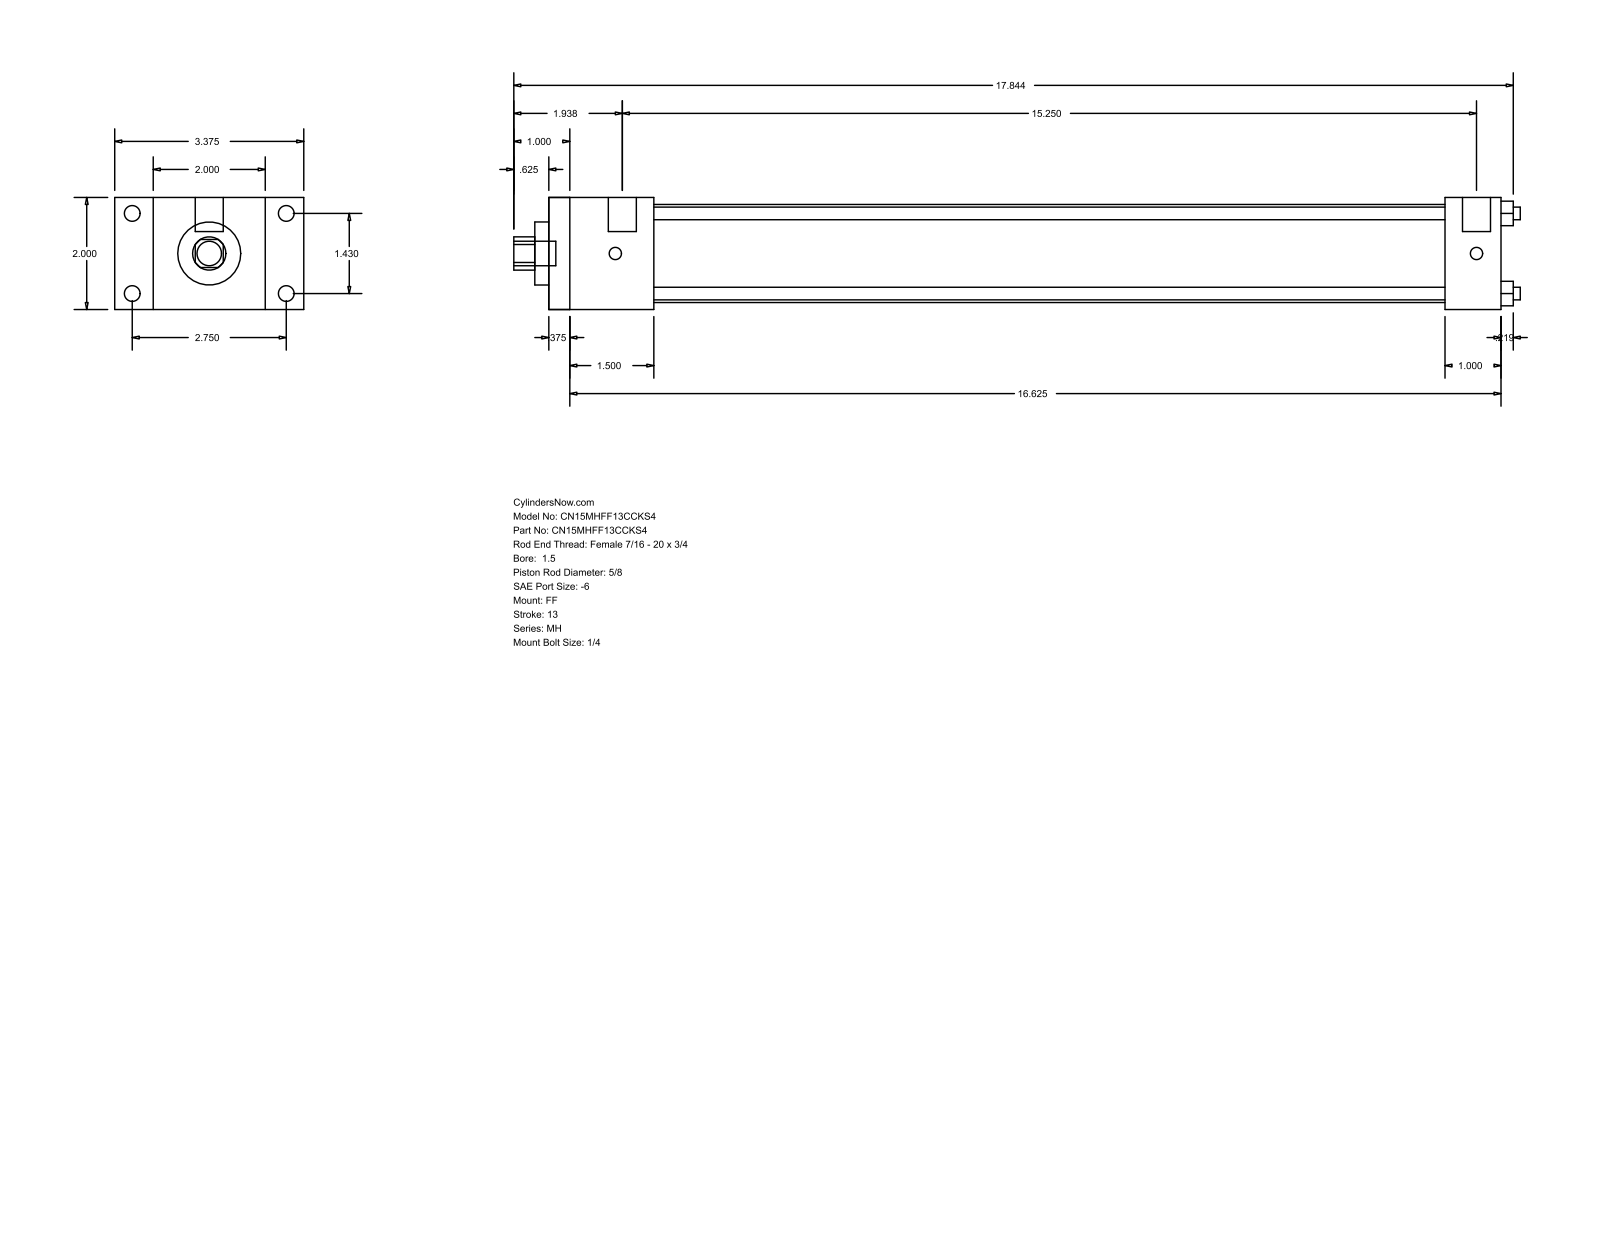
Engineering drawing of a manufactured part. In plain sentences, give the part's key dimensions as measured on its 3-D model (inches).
The part is named "MH_FF__0150_0.625". Its 3-D file was written by "GSSL Pune (CONFIG_CONTROL_DESIGN)". It is 0 solids with 92 faces: 64 planar, 28 cylindrical and 0 other. Overall it measures 17.969 by 3.375 by 2 inches. Round holes: 4 of diameter 0.225, 1 of diameter 0.625, 1 of diameter 1.125, 1 of diameter 1.75. Round bosses or shafts: 4 of diameter 0.281, 4 of diameter 0.219, 2 of diameter 0.5, 1 of diameter 0.437. Partial cylindrical surfaces (rounded edges, fillets, slot ends): 1 of radius 0.297. The main face-to-face distances are 2, 17, 0.375, 16.625, 0.687, 2.687, 1.875, 1.5, 15.125, 16. The hole center spacings are 1.011, 1.43, 2.022.
